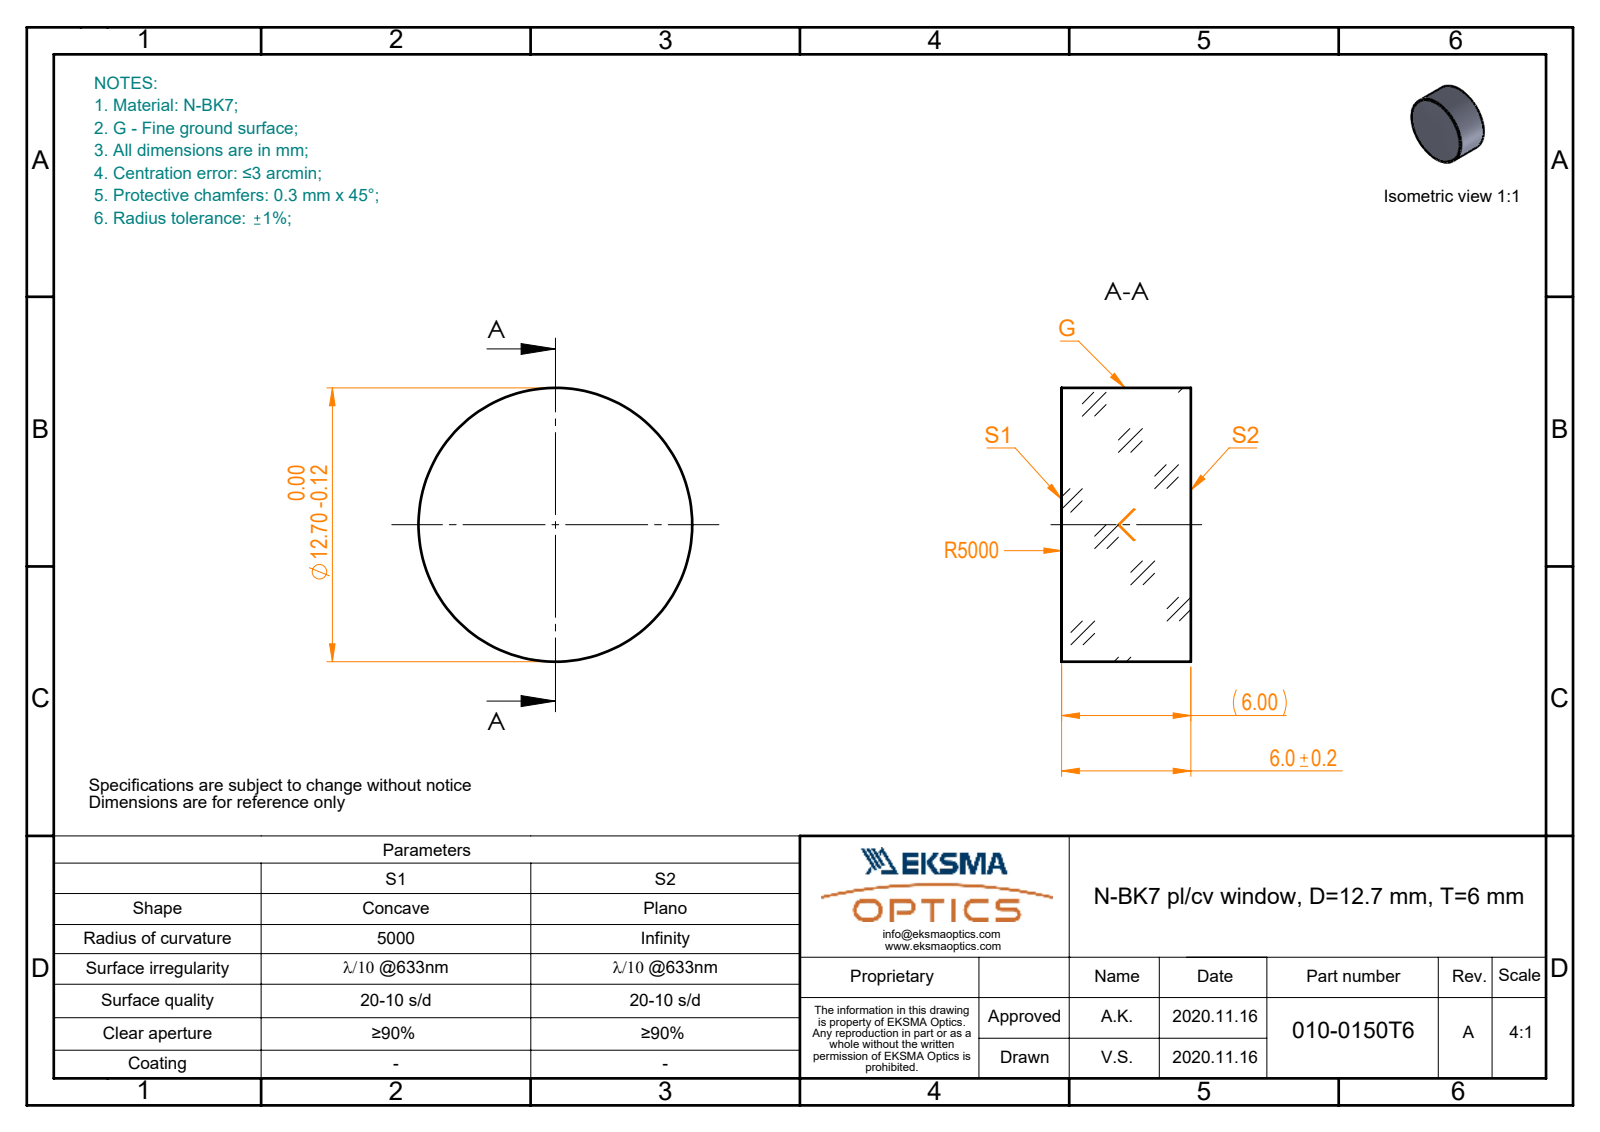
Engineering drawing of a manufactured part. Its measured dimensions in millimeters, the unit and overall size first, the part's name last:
Units: millimetres
Overall size (bounding box): 12.7 × 12.7 × 6
Round bosses / shafts (diameter × count): ⌀12.7 ×1
Volume: 760 mm³ · Surface area: 493 mm²
Bodies: 1 solid, 5 faces (1 planar, 2 cylindrical, 2 other)
Part name (STEP PRODUCT): 010-0150T6_N-BK7_PCV_window
STEP written by: SolidWorks 2019 (CONFIG_CONTROL_DESIGN)
